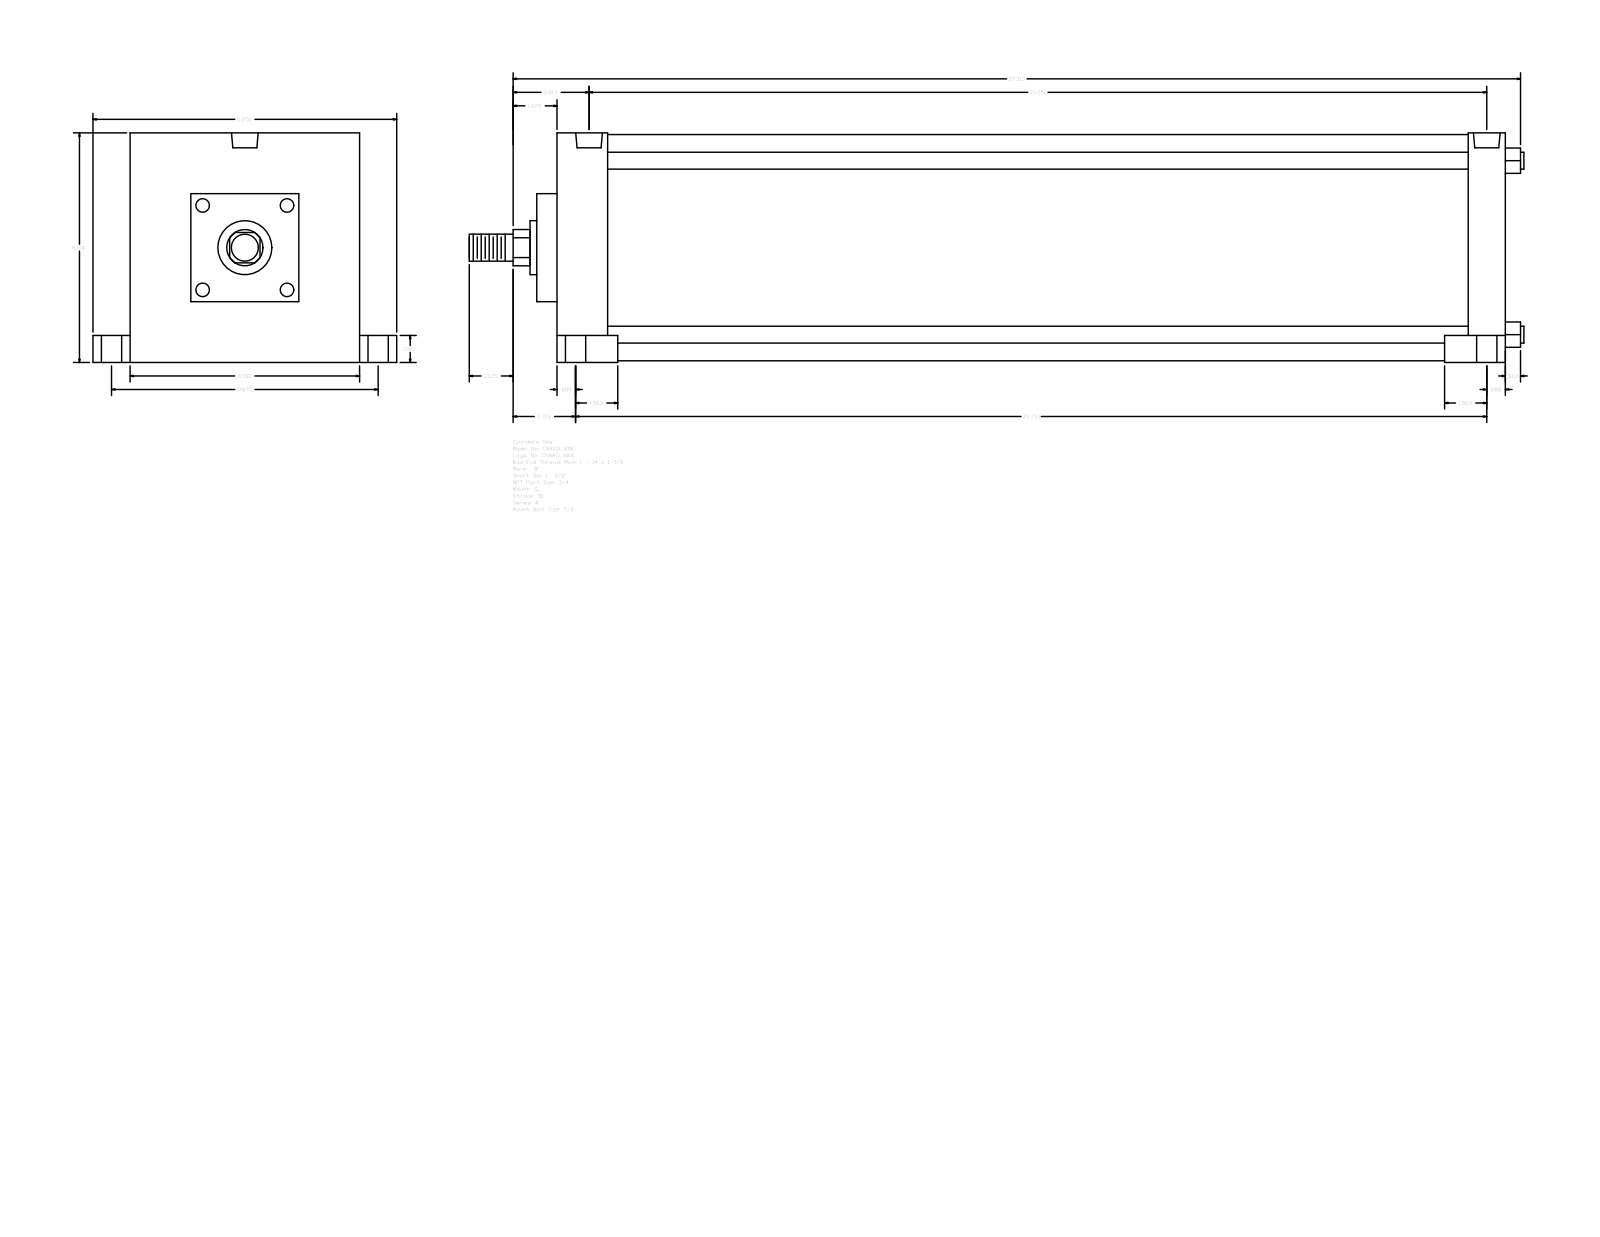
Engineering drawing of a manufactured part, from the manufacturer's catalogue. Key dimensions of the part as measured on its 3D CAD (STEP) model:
Part name (STEP PRODUCT): A_SL__0800_1.375
STEP written by: GSSL Pune (CONFIG_CONTROL_DESIGN)
Units: millimetres
Bodies: 0 solids, 117 faces (85 planar, 32 cylindrical, 0 other)
Overall size (bounding box): 992.19 × 285.75 × 215.9
Round holes (diameter × count): ⌀15.08 ×4, ⌀19.05 ×4, ⌀25.4 ×4, ⌀25.12 ×2
Round bosses / shafts (diameter × count): ⌀15.88 ×4, ⌀212.72 ×1, ⌀50.8 ×1, ⌀34.92 ×1, ⌀25.4 ×1
Partial cylindrical surfaces — rounded edges, fillets, slot ends (radius × count): R17.06 ×1
Main face-to-face distances: 892.18, 215.9, 34.93, 57.15, 47.63, 844.55, 857.25, 809.62, 19.04, 66.67
Hole centre spacings: 6.35, 125.41, 125.57, 126.05, 126.85, 250.82, 831.85, 838.2
